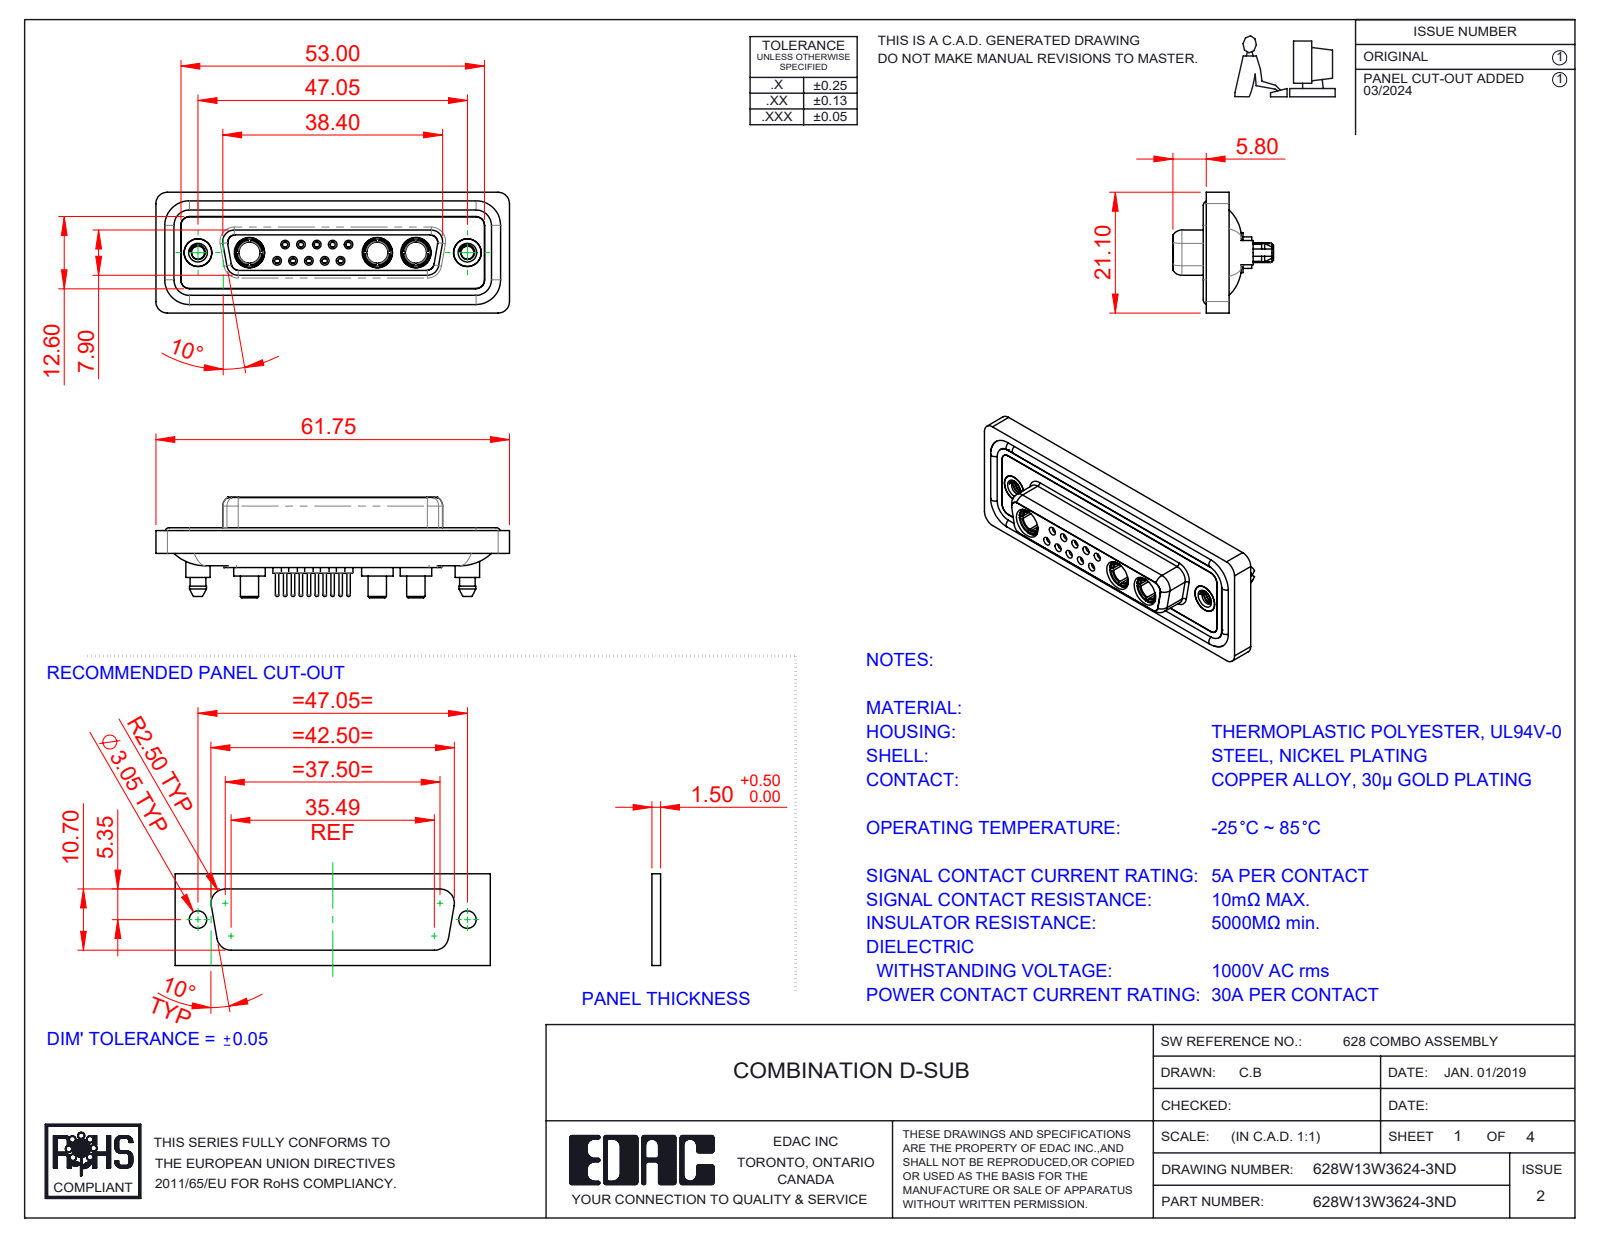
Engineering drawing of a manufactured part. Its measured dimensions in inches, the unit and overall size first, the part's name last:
Units: inches
Overall size (bounding box): 2.431 × 0.831 × 0.691
Round holes (diameter × count): ⌀0.035 ×10, ⌀0.043 ×10, ⌀0.059 ×10, ⌀0.079 ×10, ⌀0.063 ×5, ⌀0.067 ×5, ⌀0.191 ×5, ⌀0.146 ×3, ⌀0.209 ×3, ⌀0.089 ×2, ⌀0.157 ×2, ⌀0.159 ×2
Round bosses / shafts (diameter × count): ⌀0.087 ×10, ⌀0.024 ×10, ⌀0.063 ×9, ⌀0.217 ×3, ⌀0.205 ×3, ⌀0.195 ×3, ⌀0.187 ×3, ⌀0.148 ×3
Partial cylindrical surfaces — rounded edges, fillets, slot ends (radius × count): R0.059 ×24, R0.079 ×18, R0.063 ×10, R0.053 ×8, R0.01 ×4, R0.02 ×4, R0.024 ×4, R0.026 ×4
Main face-to-face distances: 0.016, 0.071, 0.293, 0.222, 0.02, 0.26, 0.278, 0.063, 0.114, 0.043
Hole centre spacings: 0.124, 0.109, 0.198, 0.198, 0.218, 0.327, 0.295, 0.109
Volume: 0.514 in³ · Surface area: 21.8 in²
Bodies: 23 solids, 1224 faces (358 planar, 495 cylindrical, 371 other)
Part name (STEP PRODUCT): 628Combo Waterproof Housing_25 Contacts; 628Combo Shell Front_25 Contacts; 628Combo Contact Row 2_24; Power Socket_30A S (+5 more)
STEP written by: SolidWorks 2023 (CONFIG_CONTROL_DESIGN)
